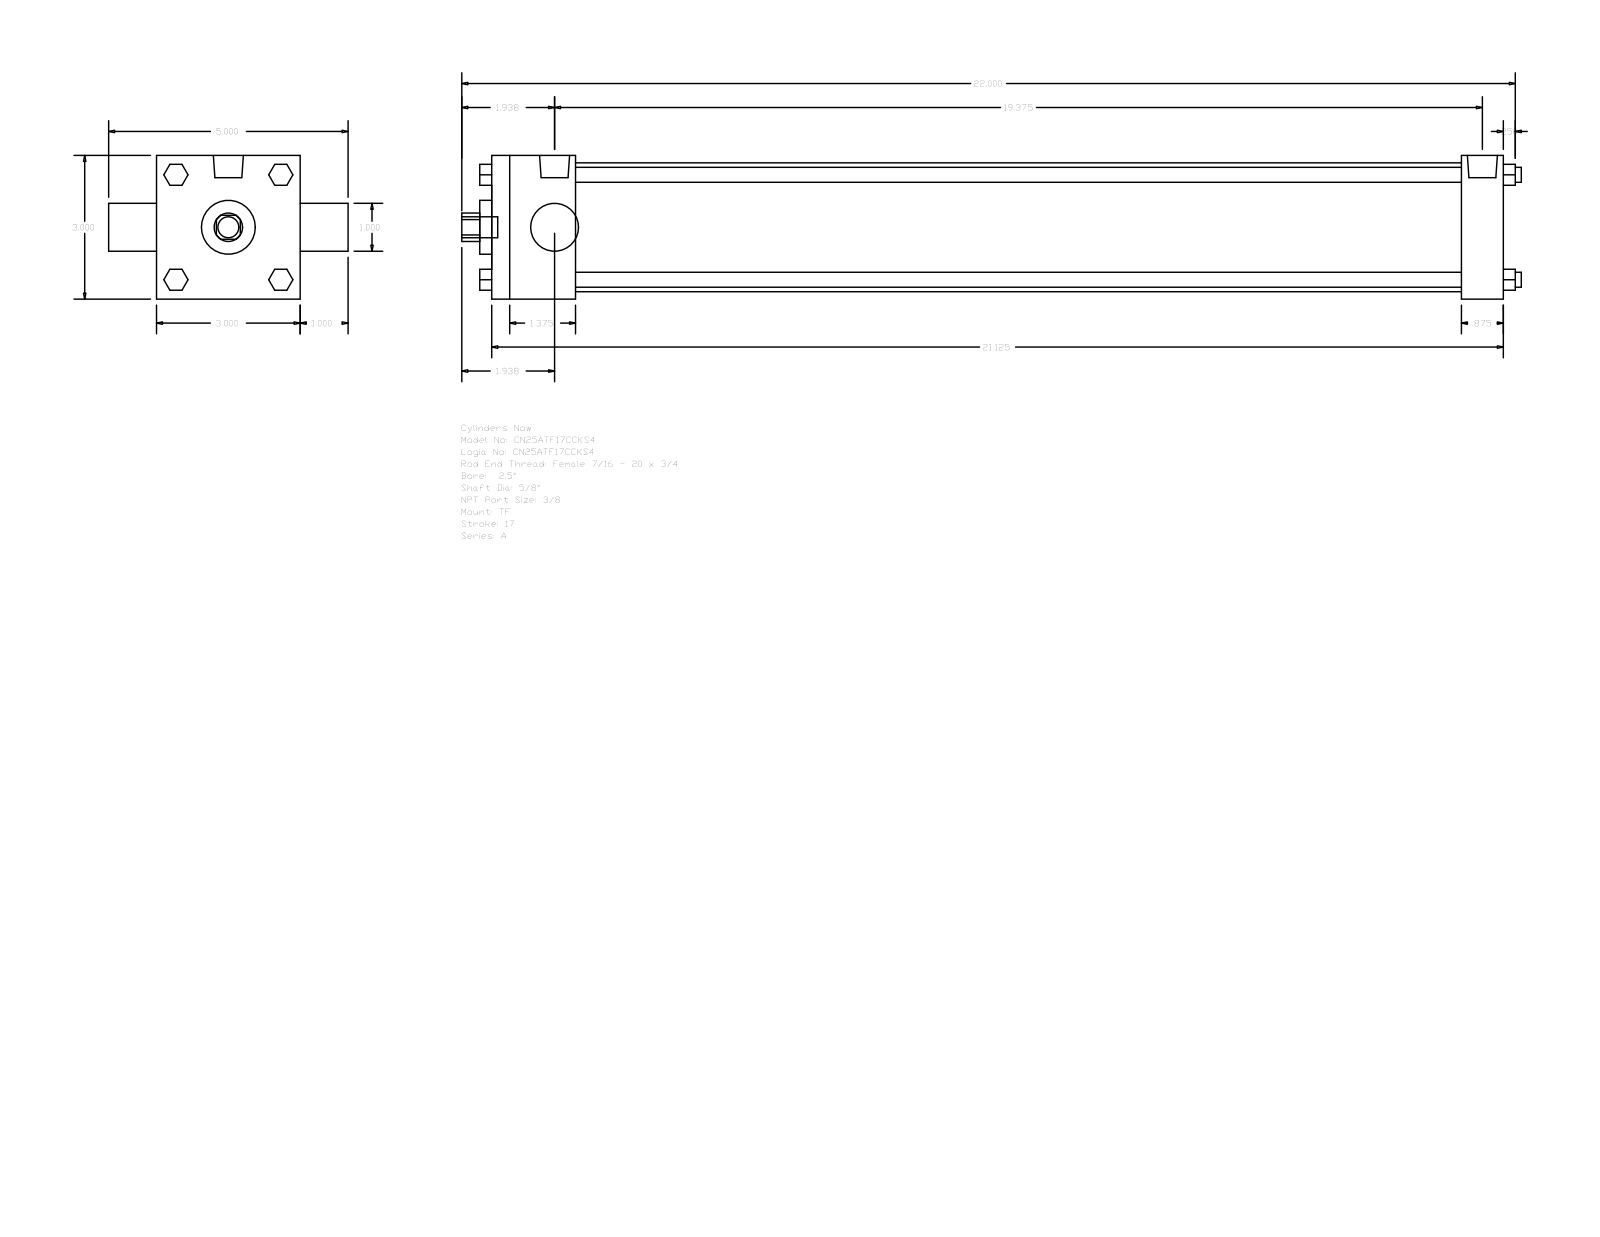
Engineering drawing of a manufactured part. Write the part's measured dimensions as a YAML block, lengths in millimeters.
part_name: "A_TF__0250_0.625"
step_written_by: "GSSL Pune (CONFIG_CONTROL_DESIGN)"
units: millimeters
bodies: {solids: 0, faces: 120, planar: 92, cylindrical: 28, other: 0}
overall_size: [561.98, 127, 76.2]
round_holes:
  - {diameter: 15.88, count: 1}
  - {diameter: 25.4, count: 1}
  - {diameter: 28.57, count: 1}
  - {diameter: 68.33, count: 1}
round_bosses_or_shafts:
  - {diameter: 7.94, count: 4}
  - {diameter: 5.56, count: 3}
  - {diameter: 15.93, count: 2}
  - {diameter: 11.11, count: 1}
partial_cylinders:
  - {radius: 7.54, count: 1}
face_to_face_distances: [76.2, 536.57, 44.45, 514.35, 469.9, 492.12, 22.22, 25.4, 101.6, 6.35]
